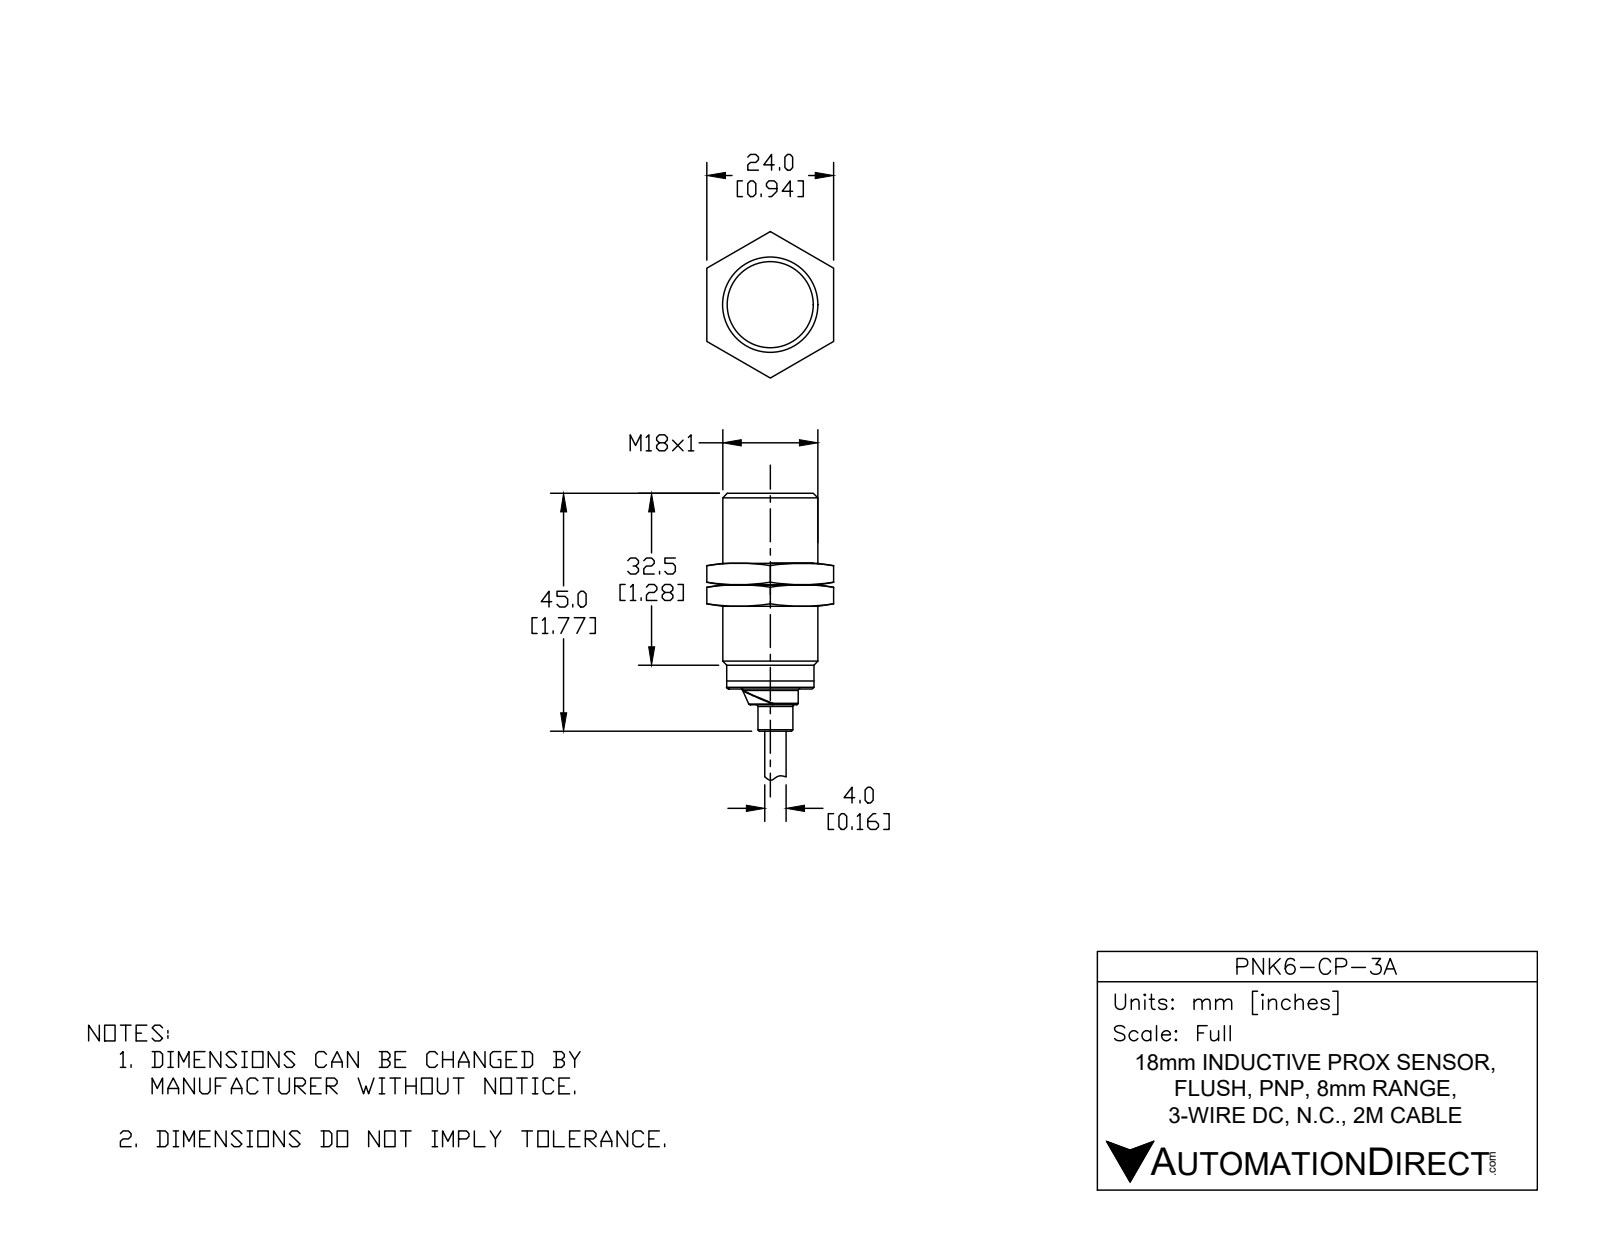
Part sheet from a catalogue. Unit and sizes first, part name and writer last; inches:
Units: inches
Overall size (bounding box): 3.272 × 0.709 × 0.709
Round holes (diameter × count): ⌀0.162 ×1
Round bosses / shafts (diameter × count): ⌀0.049 ×6, ⌀0.709 ×1, ⌀0.65 ×1, ⌀0.65 ×1, ⌀0.417 ×1, ⌀0.26 ×1, ⌀0.157 ×1
Partial cylindrical surfaces — rounded edges, fillets, slot ends (radius × count): R0.146 ×1
Main face-to-face distances: 1.457, 1.398, 0.059, 1.575, 0.177, 0.118, 1.545, 0.148, 0.089, 0.03
Volume: 0.61 in³ · Surface area: 5.425 in²
Bodies: 1 solid, 78 faces (19 planar, 27 cylindrical, 32 other)
Part name (STEP PRODUCT): PNK6-CP-3A
STEP written by: SolidWorks 2017 (AUTOMOTIVE_DESIGN)
